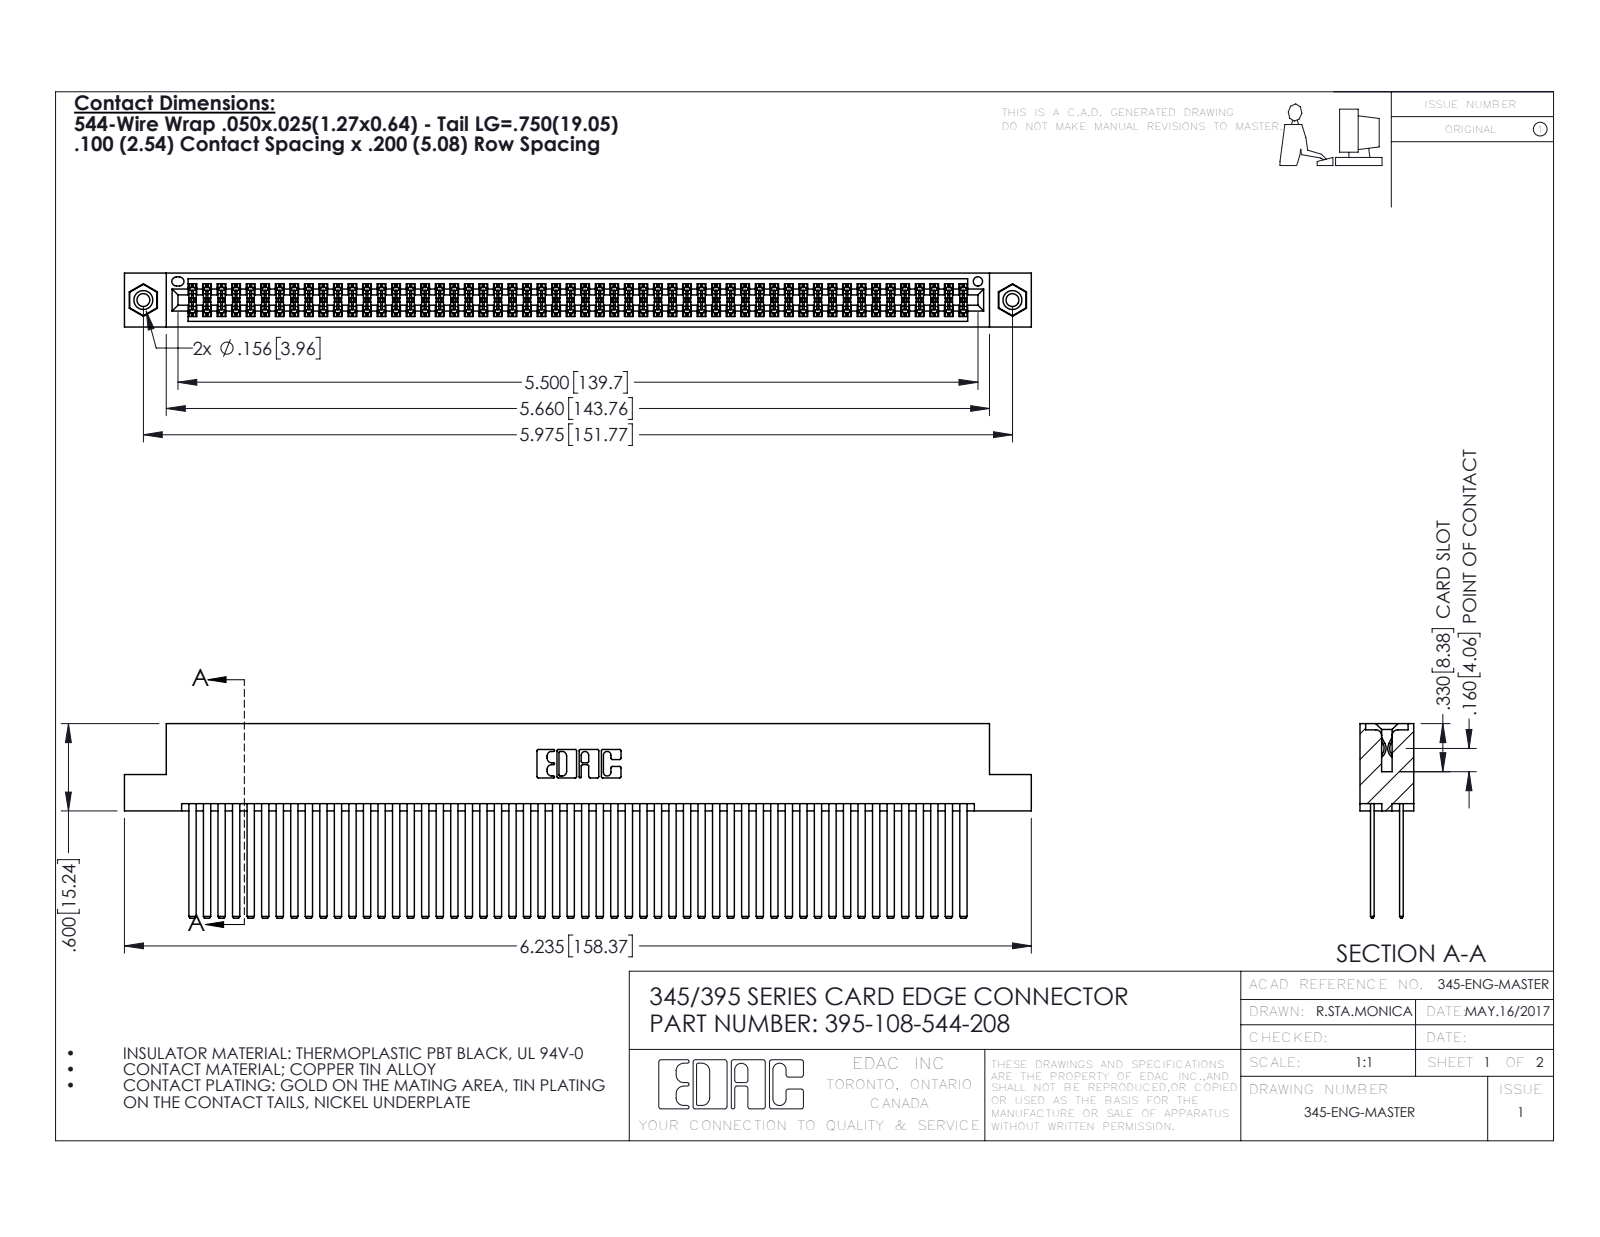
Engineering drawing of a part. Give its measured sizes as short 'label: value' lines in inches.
name: 395-108-544-208; 345 Part_Flush Mounting Lugs - 0.156 Dia-TI; 345-292-001_345-293-144; 345-250-001_345-250-003-102
written by: SolidWorks 2016 (CONFIG_CONTROL_DESIGN)
unit: in
bodies: 111 solids, 4938 faces (3244 planar, 1678 cylindrical, 16 other)
size: 6.235 × 1.337 × 0.37
volume: 1.038 in³; area: 46.22 in²
holes: 2× ⌀0.089, 2× ⌀0.125, 2× ⌀0.156, 1× ⌀0.064
bosses: 2× ⌀0.155
rounds: 162× R0.006, 22× R0.01, 6× R0.007, 6× R0.031, 3× R0.026, 2× R0.014, 2× R0.019, 2× R0.022
face distances: 0.2, 0.025, 0.072, 0.098, 0.272, 0.298, 0.225, 0.175, 0.37, 0.05
hole spacings: 0.27, 5.739, 5.975
